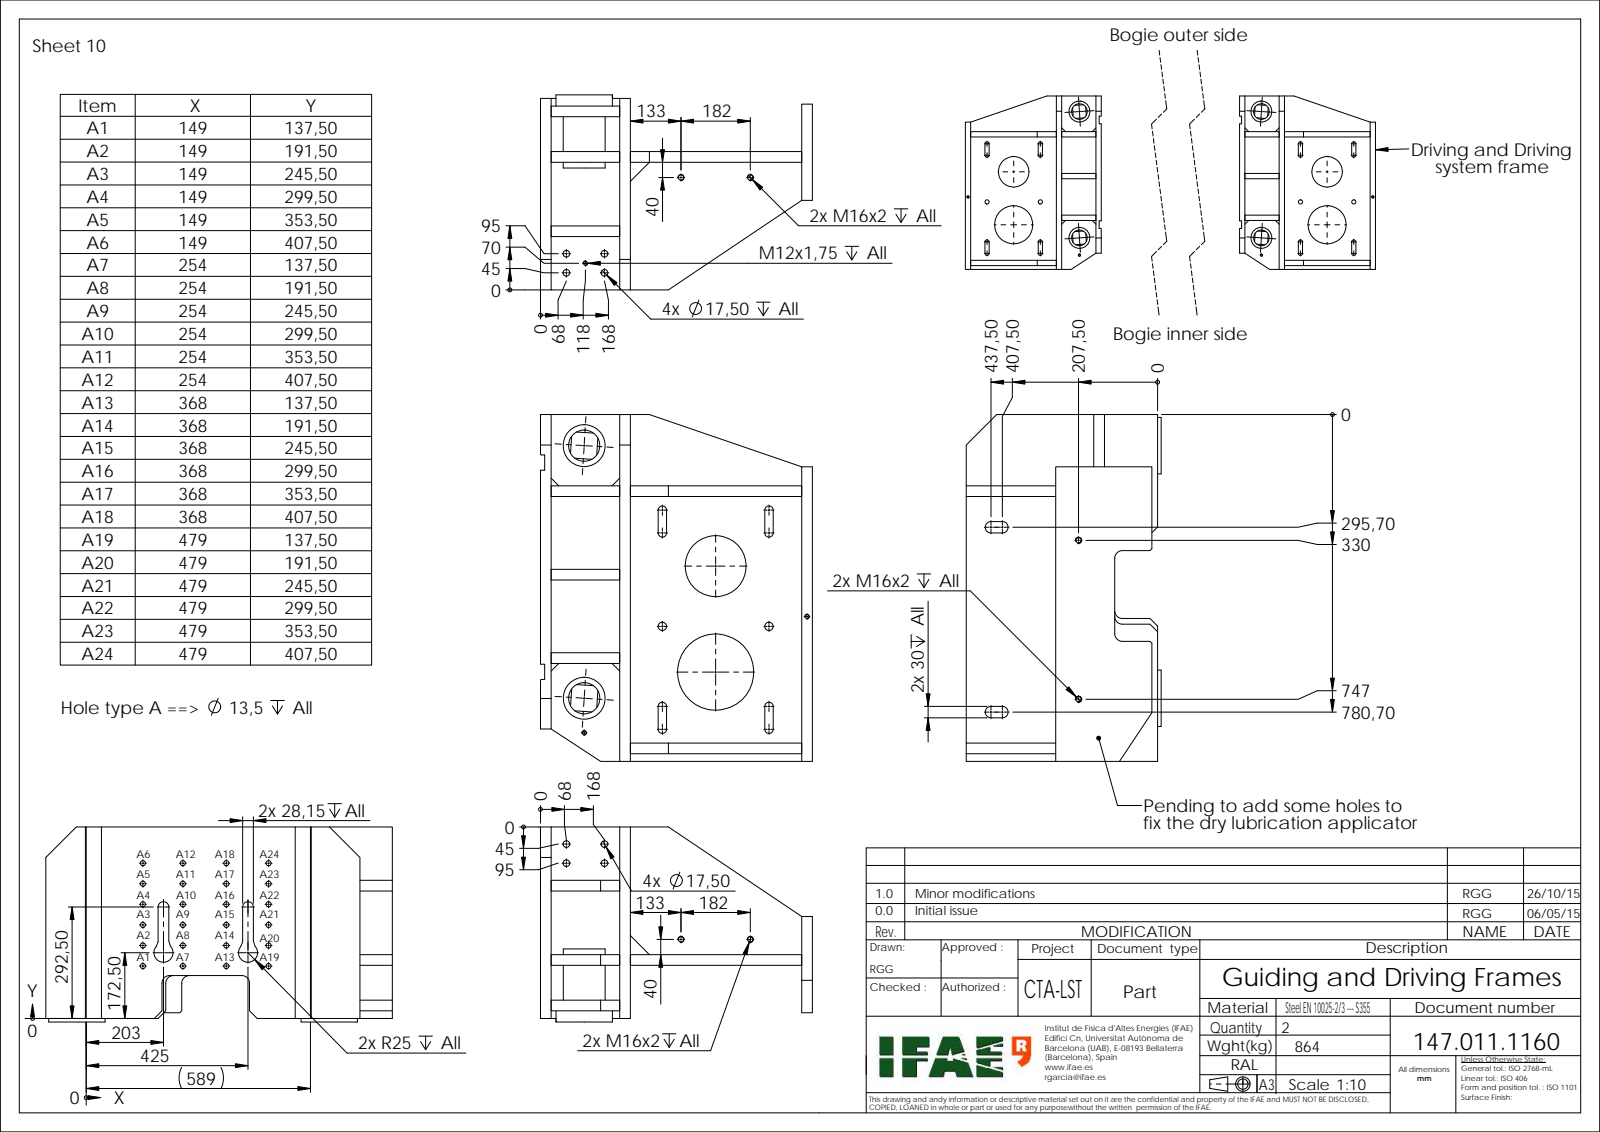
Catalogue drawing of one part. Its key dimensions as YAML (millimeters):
part_name: "147.011.1160 20160204"
step_written_by: "SolidWorks 2014 (AUTOMOTIVE_DESIGN)"
units: millimeters
bodies: {solids: 34, faces: 704, planar: 368, cylindrical: 308, other: 28}
overall_size: [2698, 910, 511.8]
volume: 110400000
surface_area: 9865000
round_holes:
  - {diameter: 13.5, count: 24}
  - {diameter: 5, count: 12}
  - {diameter: 17.5, count: 8}
  - {diameter: 10.2, count: 6}
  - {diameter: 14, count: 6}
  - {diameter: 22, count: 4}
  - {diameter: 82, count: 4}
  - {diameter: 110, count: 4}
  - {diameter: 160, count: 2}
  - {diameter: 200, count: 2}
round_bosses_or_shafts:
  - {diameter: 148, count: 4}
partial_cylinders:
  - {radius: 11, count: 16}
  - {radius: 20, count: 6}
  - {radius: 15, count: 4}
  - {radius: 25, count: 2}
  - {radius: 14, count: 1}
  - {radius: 14.07, count: 1}
face_to_face_distances: [28, 208, 1506, 1714, 180, 1534, 478, 686, 1984, 2192]
hole_center_spacings: [54, 108, 162, 118.07, 123.44, 126.14, 225.56, 231.39]
